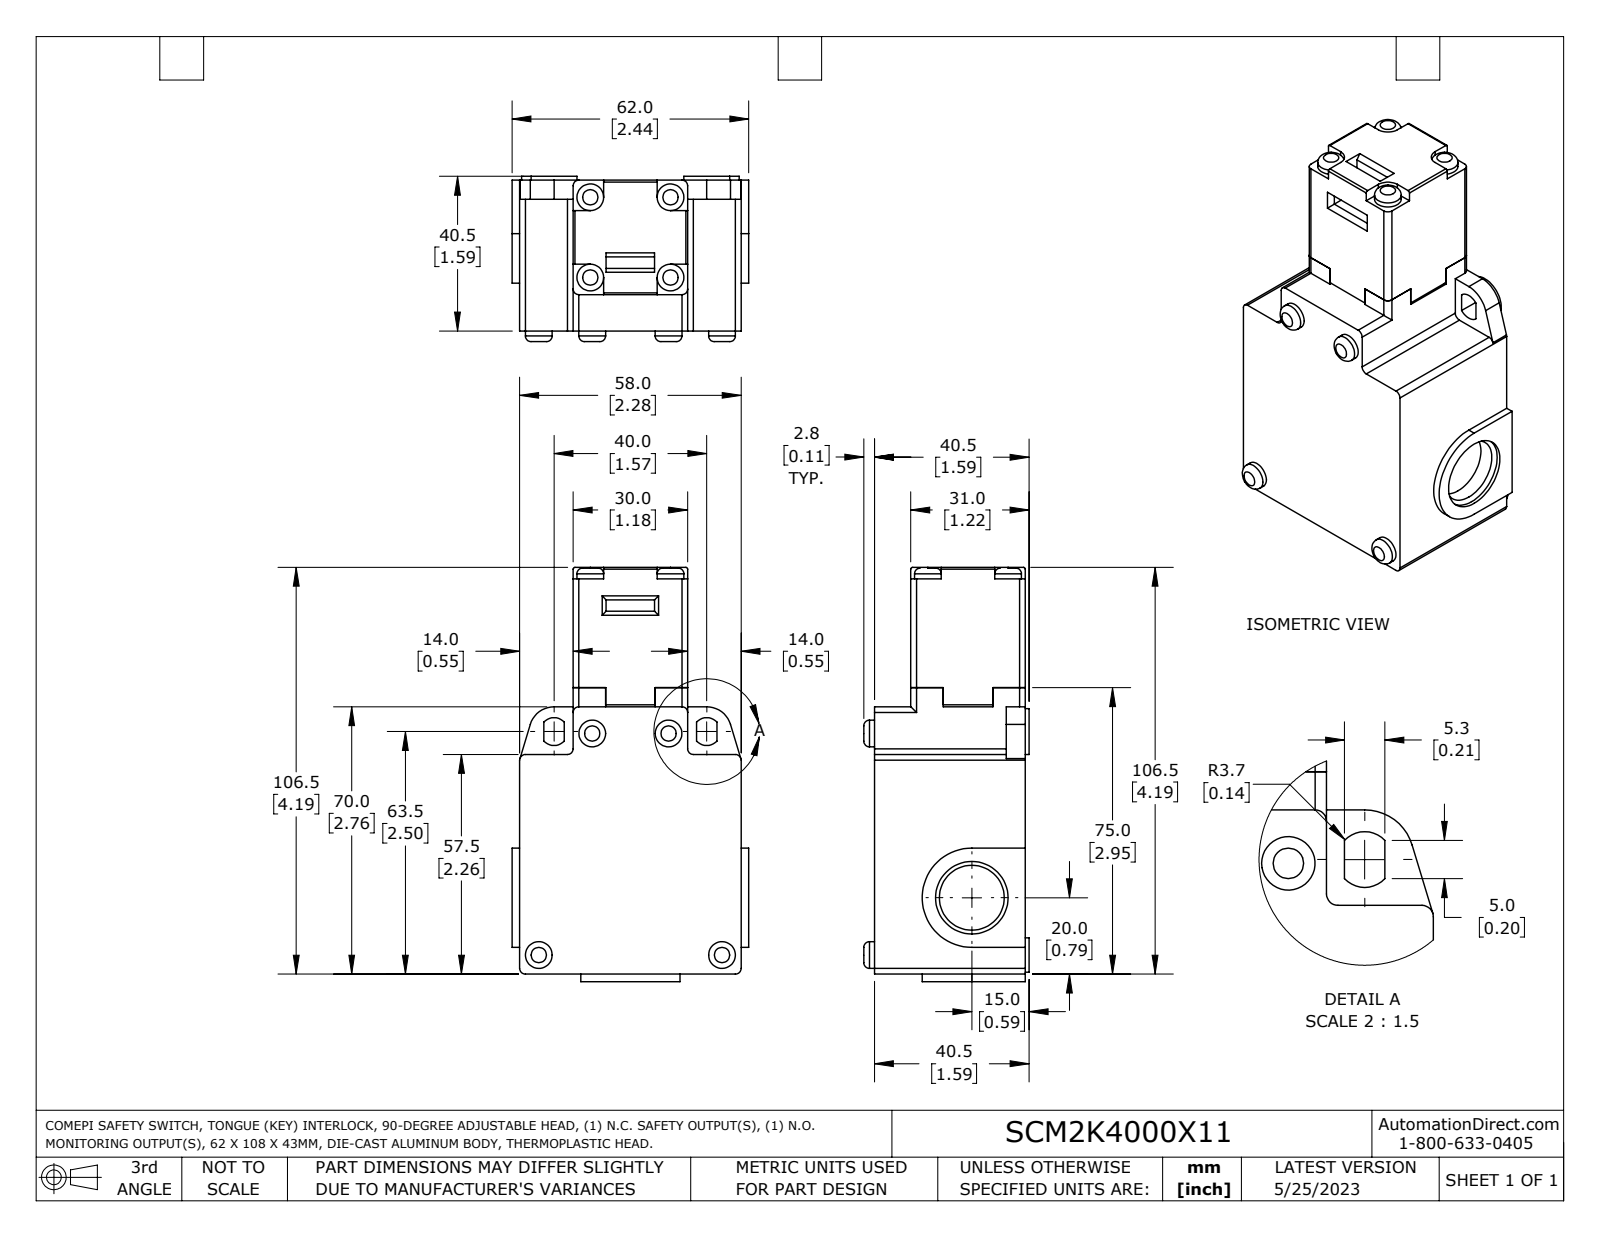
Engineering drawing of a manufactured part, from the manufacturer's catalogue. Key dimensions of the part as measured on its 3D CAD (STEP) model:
Part name (STEP PRODUCT): SCM2K4000X11
STEP written by: SolidWorks 2021 (AUTOMOTIVE_DESIGN)
Units: inches
Bodies: 2 solids, 176 faces (106 planar, 59 cylindrical, 11 other)
Overall size (bounding box): 4.272 × 2.441 × 1.705
Volume: 10.84 in³ · Surface area: 43.53 in²
Round holes (diameter × count): ⌀0.276 ×4, ⌀0.669 ×2, ⌀0.748 ×2
Round bosses / shafts (diameter × count): ⌀0.276 ×4, ⌀0.472 ×2, ⌀0.354 ×2
Partial cylindrical surfaces — rounded edges, fillets, slot ends (radius × count): R0.059 ×12, R0.02 ×4, R0.144 ×2, R0.256 ×2, R0.512 ×2, R0.453 ×1, R0.472 ×1
Main face-to-face distances: 1.555, 1.732, 0.551, 1.181, 2.283, 0.079, 0.236, 0.374, 2.756, 0.118
Hole centre spacings: 0.827, 0.557, 0.613, 1.169
